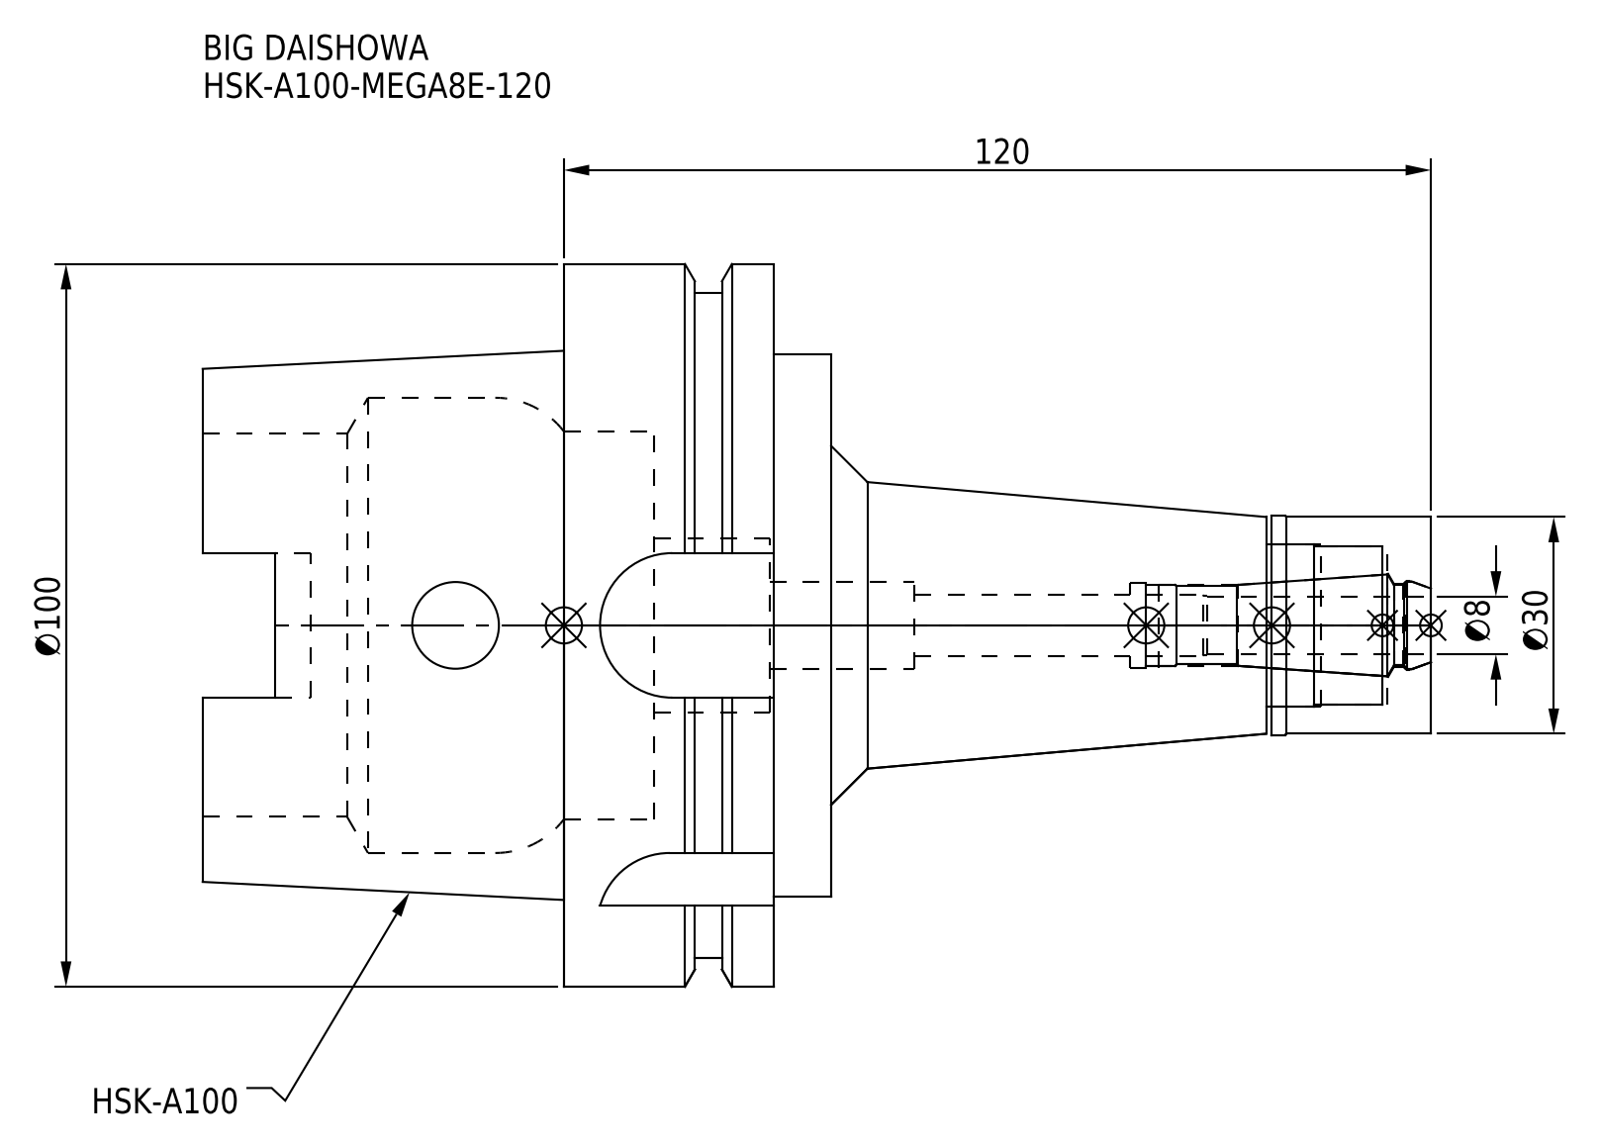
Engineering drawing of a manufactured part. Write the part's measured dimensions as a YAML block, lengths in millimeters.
part_name: "MEN8_1.stp; HSK-A100-MEGA8E-120_1.stp; HSK-A100-MEGA8E-120-080-FreeParts; HSK-A100-MEGA8E-120-080.stp (+3 more)"
step_written_by: "SolidWorks 2019 (CONFIG_CONTROL_DESIGN)"
units: millimeters
bodies: {solids: 2, faces: 126, planar: 42, cylindrical: 56, other: 28}
overall_size: [170, 100, 100]
volume: 356817
surface_area: 66211
round_holes:
  - {diameter: 12, count: 2}
  - {diameter: 8.4, count: 1}
  - {diameter: 11.2, count: 1}
  - {diameter: 11.4, count: 1}
  - {diameter: 11.8, count: 1}
  - {diameter: 12.3, count: 1}
  - {diameter: 22, count: 1}
  - {diameter: 22.5, count: 1}
  - {diameter: 24, count: 1}
  - {diameter: 53, count: 1}
  - {diameter: 53.8, count: 1}
  - {diameter: 63, count: 1}
round_bosses_or_shafts:
  - {diameter: 100, count: 1}
  - {diameter: 92, count: 1}
  - {diameter: 75, count: 1}
  - {diameter: 30.3, count: 1}
  - {diameter: 30, count: 1}
partial_cylinders:
  - {radius: 4.88, count: 4}
  - {radius: 10, count: 4}
face_to_face_distances: [29, 8, 37, 24.55, 16.55, 12.45, 87, 79, 62.45, 50]
